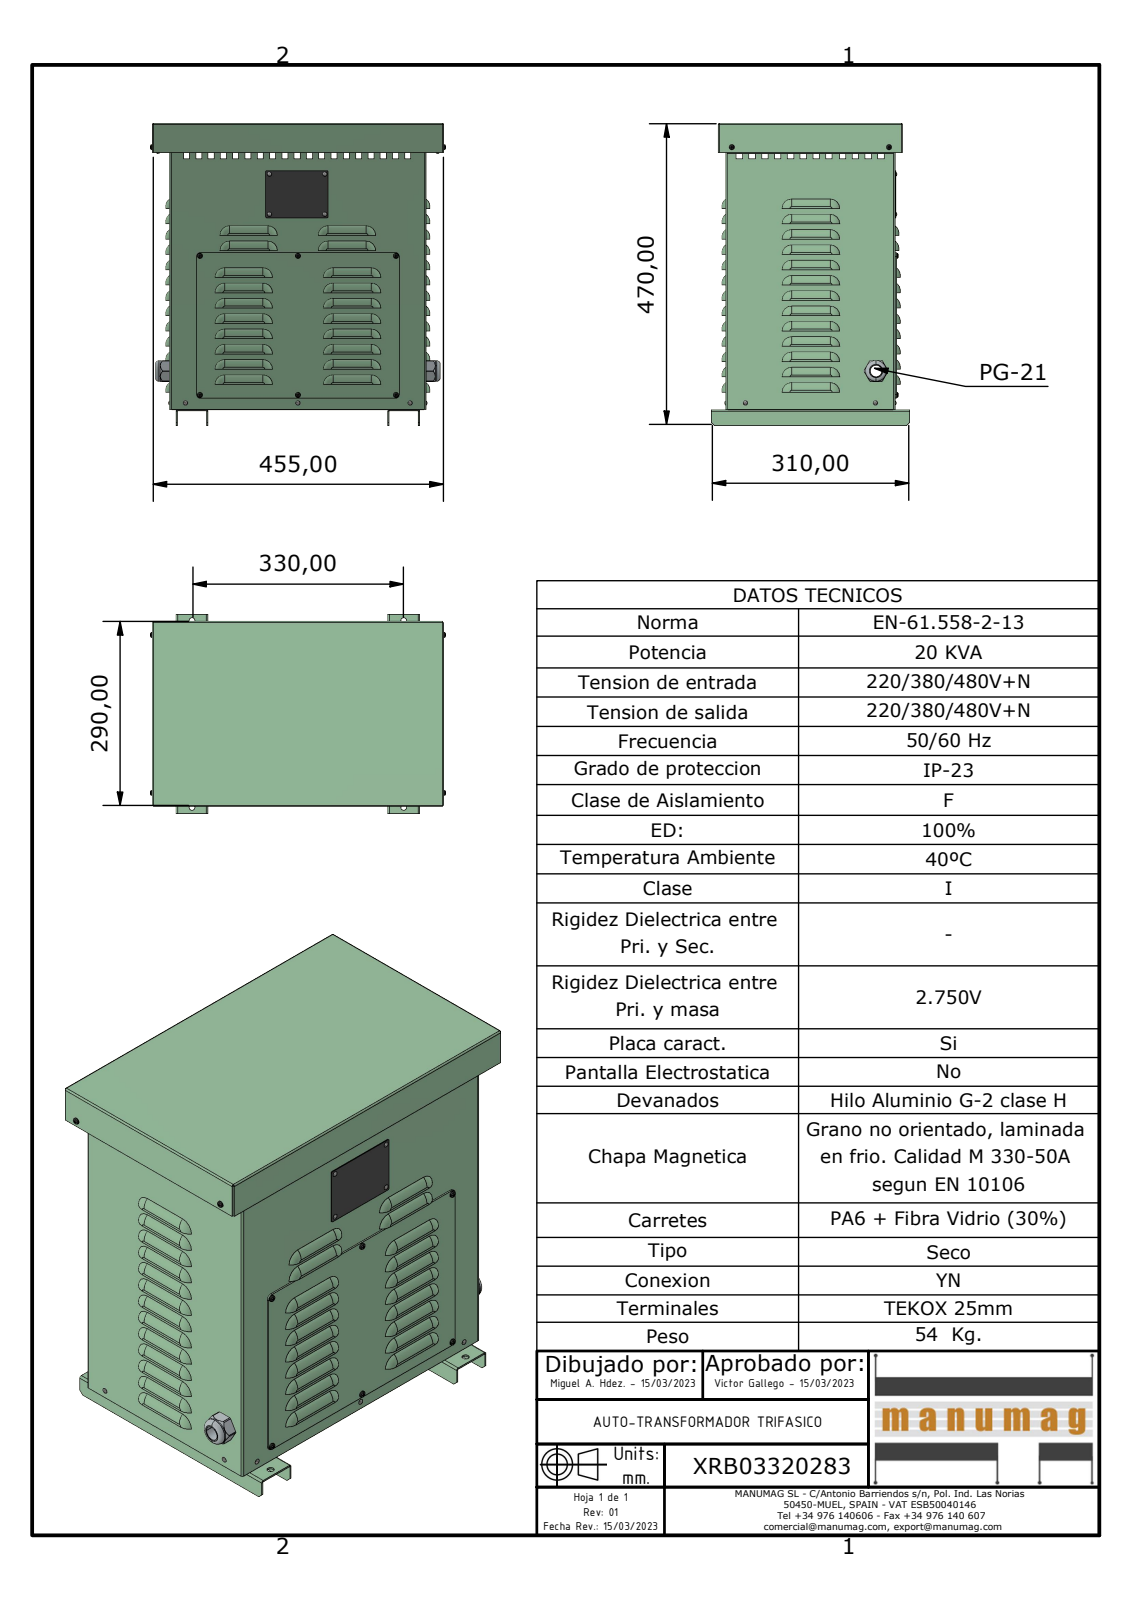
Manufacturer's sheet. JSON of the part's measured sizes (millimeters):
{"part_name": "XRB03320283; JE015 - JE020 - JE025 EXPORT CUERPO; JE015 - JE020 - JE025 EXPORT BASE; JE015 - JE020 - JE025 EXPORT PATA (+6 more)", "step_written_by": "Autodesk Inventor 2023 (AUTOMOTIVE_DESIGN)", "units": "millimeters", "bodies": {"solids": 33, "faces": 2242, "planar": 1225, "cylindrical": 489, "other": 528}, "overall_size": [474.44, 463.69, 310], "volume_mm3": 2342000, "surface_area_mm2": 2098000, "round_holes": [[3.4, 17], [4, 9], [2.3, 8], [9, 6], [5.1, 3], [8.92, 2], [18, 1], [29.9, 1]], "round_bosses_or_shafts": [[3.2, 9], [4, 8], [3.62, 8], [32.4, 1], [28.5, 1], [28.3, 1]], "partial_cylinders_radius": [[14, 118], [4, 63], [15, 49], [2, 10], [2, 9], [3.47, 8], [0.5, 6], [2.5, 6]], "face_to_face_distances": [2, 262.92, 264.92, 400.8, 447.27, 449.27, 260.92, 398.8, 402.8, 4], "hole_center_spacings": [218.1, 153.8, 154.1, 266.87, 267.05, 307.9, 332.28, 377.32]}
